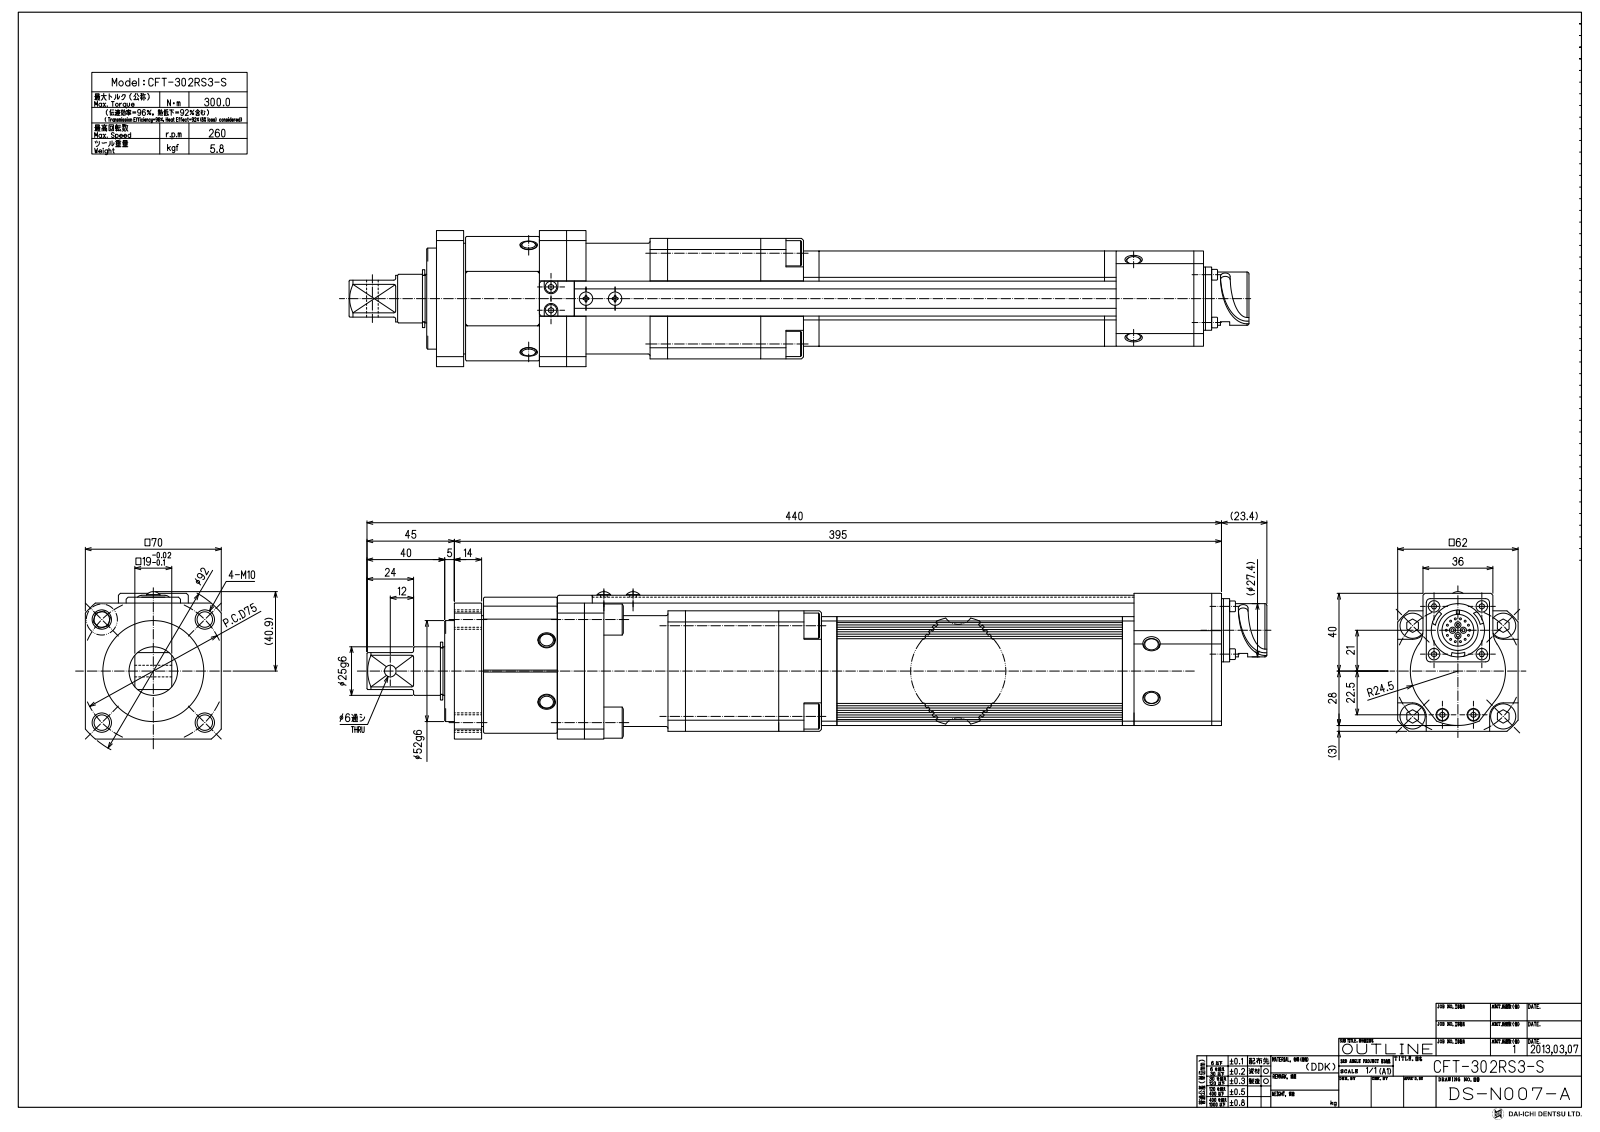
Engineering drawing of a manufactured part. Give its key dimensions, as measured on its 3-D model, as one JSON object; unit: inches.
{"part_name": "CFT-302RS3-S", "step_written_by": "SolidWorks 2013 (CONFIG_CONTROL_DESIGN)", "units": "inches", "bodies": {"solids": 13, "faces": 210, "planar": 107, "cylindrical": 80, "other": 23}, "overall_size": [18.205, 2.953, 2.756], "volume_in3": 72.37, "surface_area_in2": 256.3, "round_holes": [[0.335, 4], [0.236, 1], [0.819, 1]], "round_bosses_or_shafts": [[2.52, 1], [2.244, 1], [2.047, 1], [1.079, 1], [0.984, 1]], "partial_cylinders_radius": [[0.079, 4], [0.472, 2], [0.965, 1], [1.102, 1], [1.575, 1], [1.811, 1]], "face_to_face_distances": [2.598, 2.087, 2.756, 0.551, 0.157, 2.441, 2.047, 0.197, 3.937, 4.488], "hole_center_spacings": [2.088, 1.067, 2.143, 2.953]}
